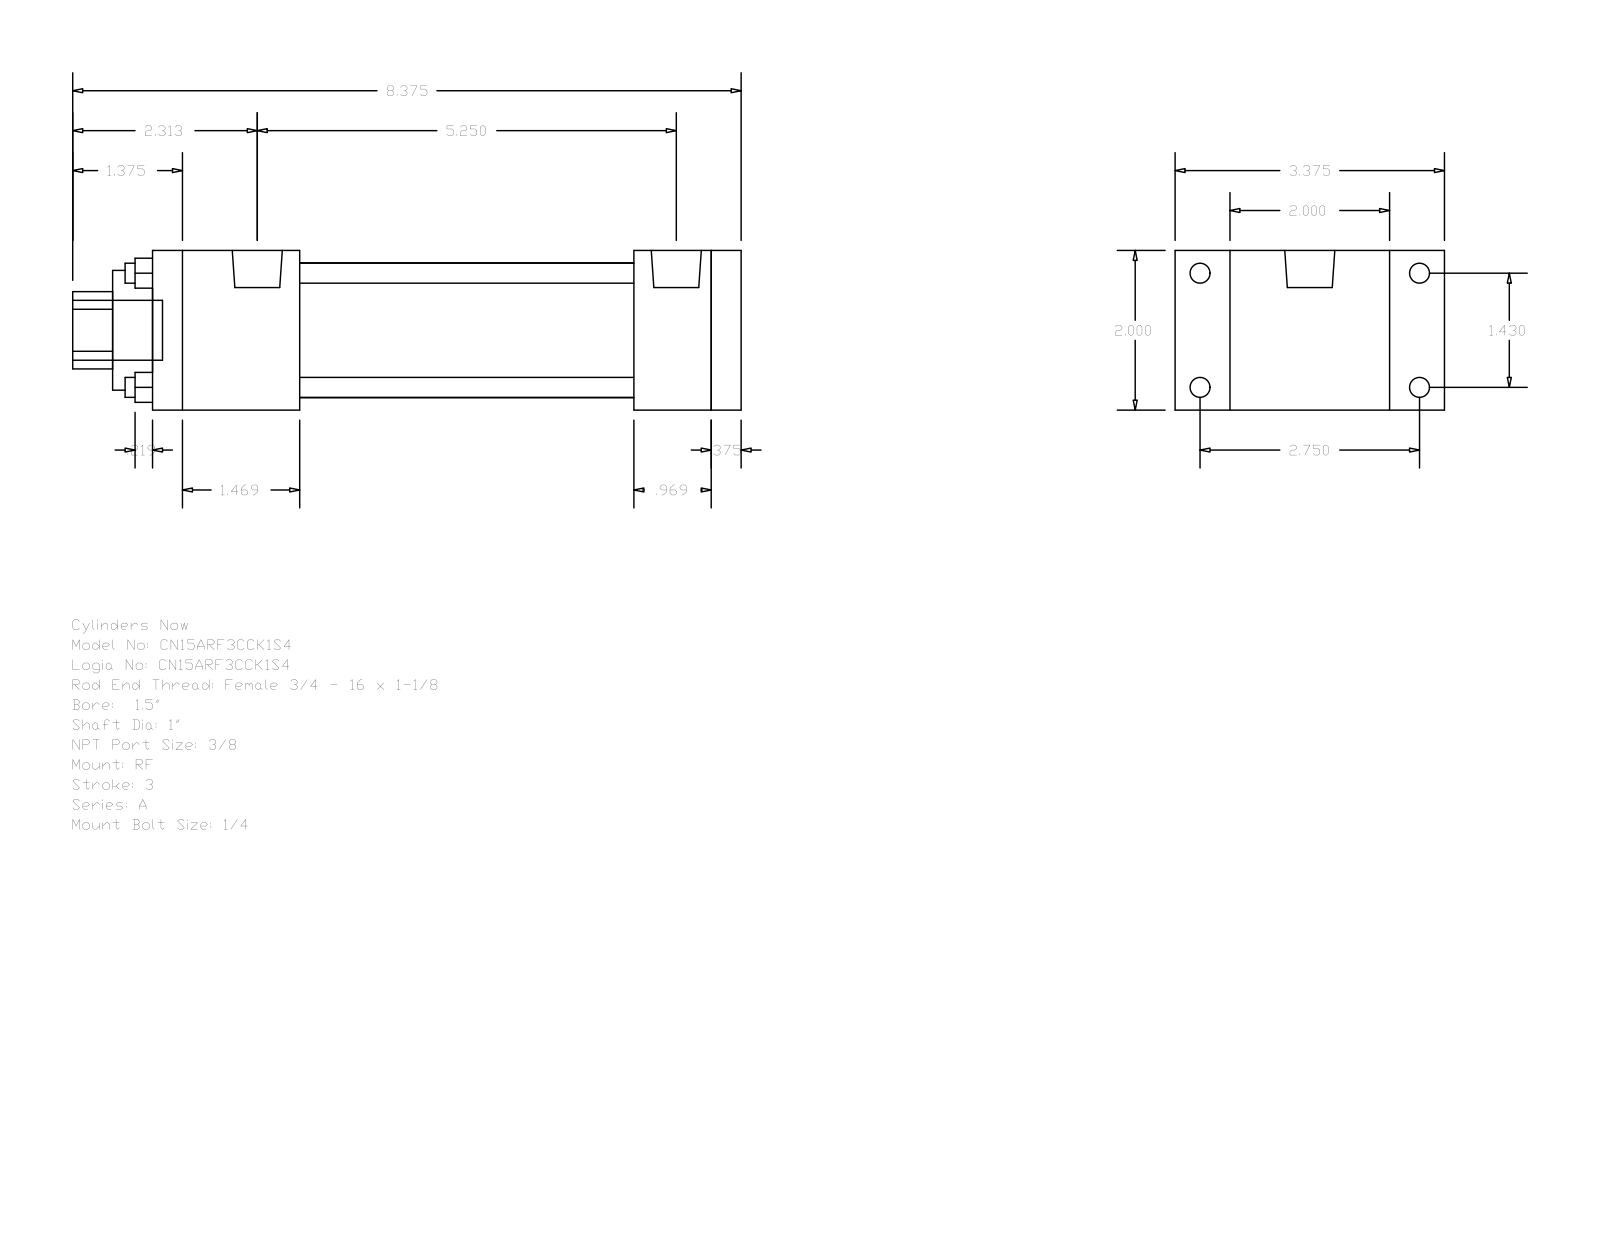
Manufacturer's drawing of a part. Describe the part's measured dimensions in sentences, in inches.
The part is named "A_RF__0150_1". Its 3-D file was written by "GSSL Pune (CONFIG_CONTROL_DESIGN)". It is 0 solids with 92 faces: 64 planar, 28 cylindrical and 0 other. Overall it measures 8.375 by 3.375 by 2 inches. Round holes: 4 of diameter 0.25, 1 of diameter 1, 1 of diameter 1.5, 1 of diameter 1.69. Round bosses or shafts: 4 of diameter 0.25, 4 of diameter 0.219, 2 of diameter 0.627, 1 of diameter 0.75. Partial cylindrical surfaces (rounded edges, fillets, slot ends): 1 of radius 0.484. The main face-to-face distances are 2, 0.375, 7, 7.375, 6.031, 0.969, 1.344, 1.844, 4.187, 5.156. The hole center spacings are 1.011, 1.43, 2.022.
